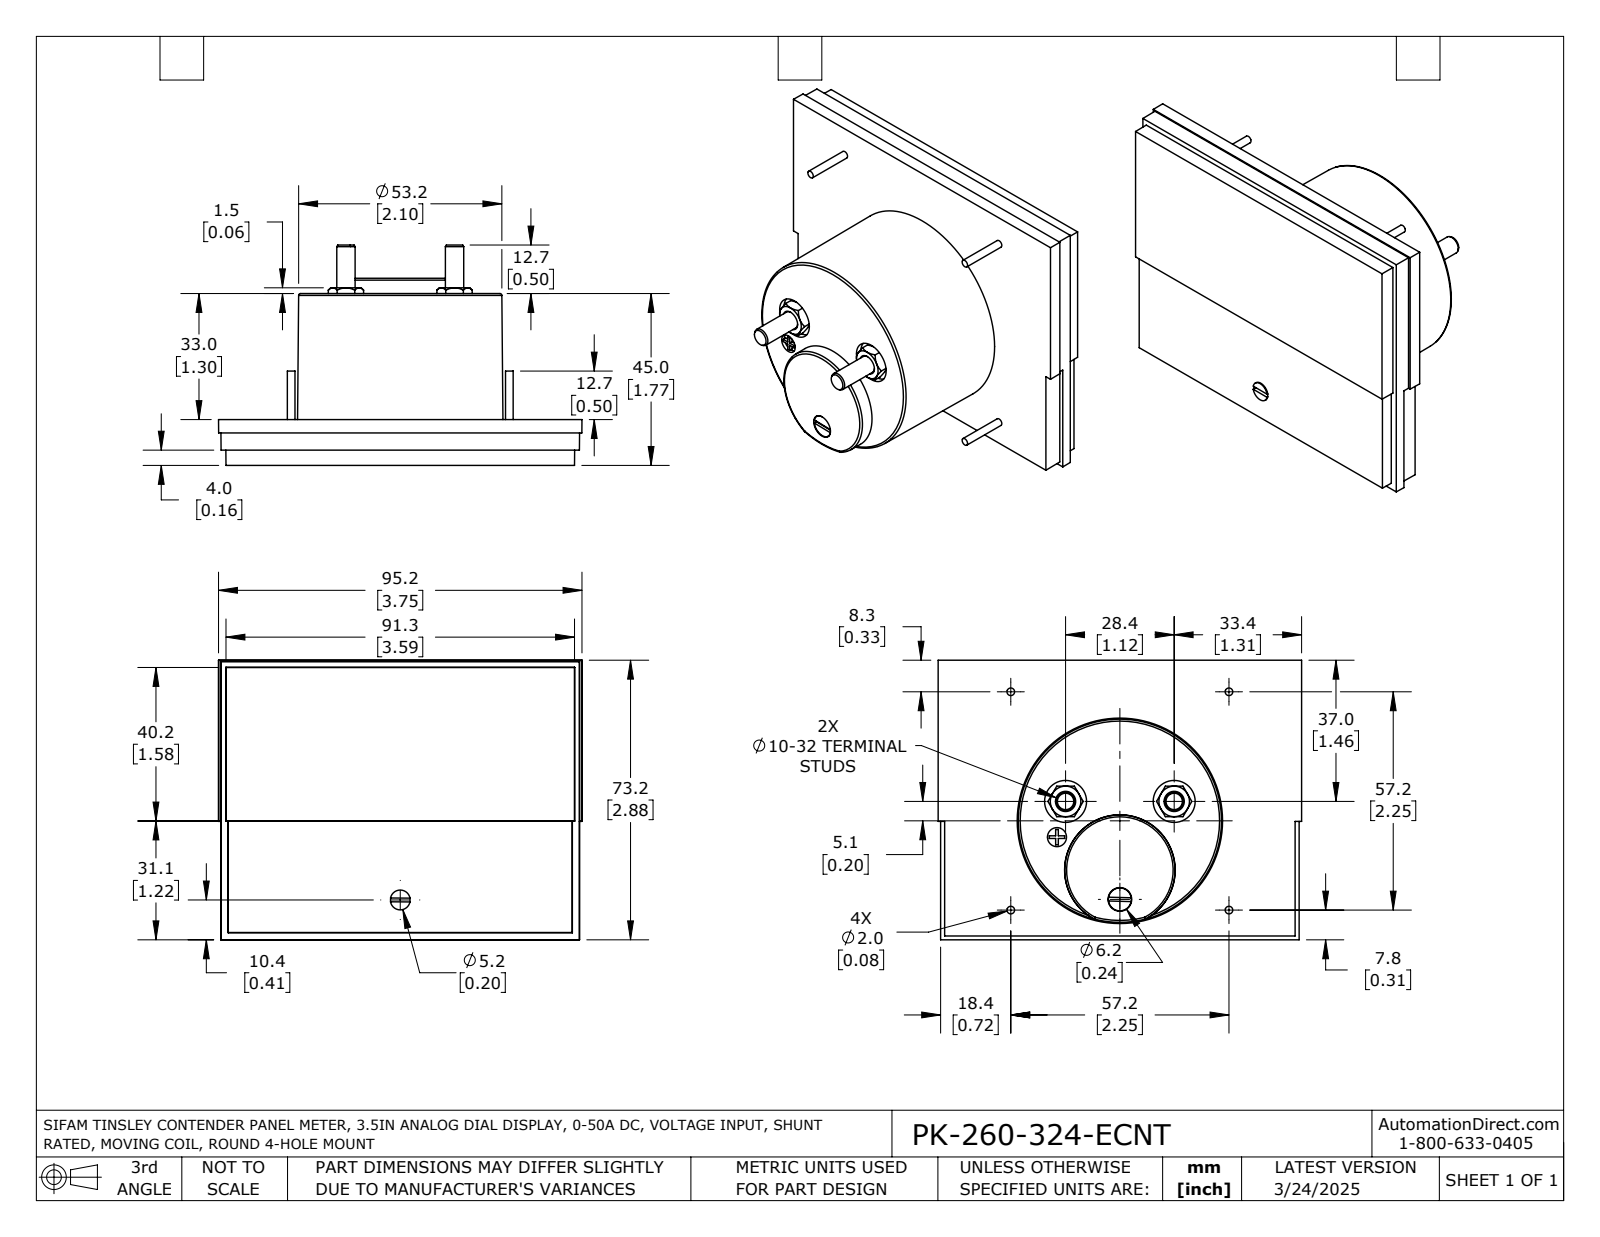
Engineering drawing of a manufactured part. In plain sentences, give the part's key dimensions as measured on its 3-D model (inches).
The part is named "PK-260-324-ECNT". Its 3-D file was written by "SolidWorks 2021 (AUTOMOTIVE_DESIGN)". It is 1 solid with 163 faces: 76 planar, 31 cylindrical and 56 other. Overall it measures 3.748 by 2.882 by 2.272 inches. Its volume is 9.446 cubic inches and its surface area 38.39 square inches. Round holes: 2 of diameter 0.433, 1 of diameter 0.197, 1 of diameter 0.244. Round bosses or shafts: 4 of diameter 0.079, 2 of diameter 0.189, 1 of diameter 0.236, 1 of diameter 0.205. Partial cylindrical surfaces (rounded edges, fillets, slot ends): 1 of radius 0.1. The main face-to-face distances are 0.472, 0.03, 0.443, 1.772, 1.299, 1.742, 0.157, 0.073, 0.315, 1.457. The hole center spacings are 1.155, 0.379, 0.912, 1.12, 1.263.
